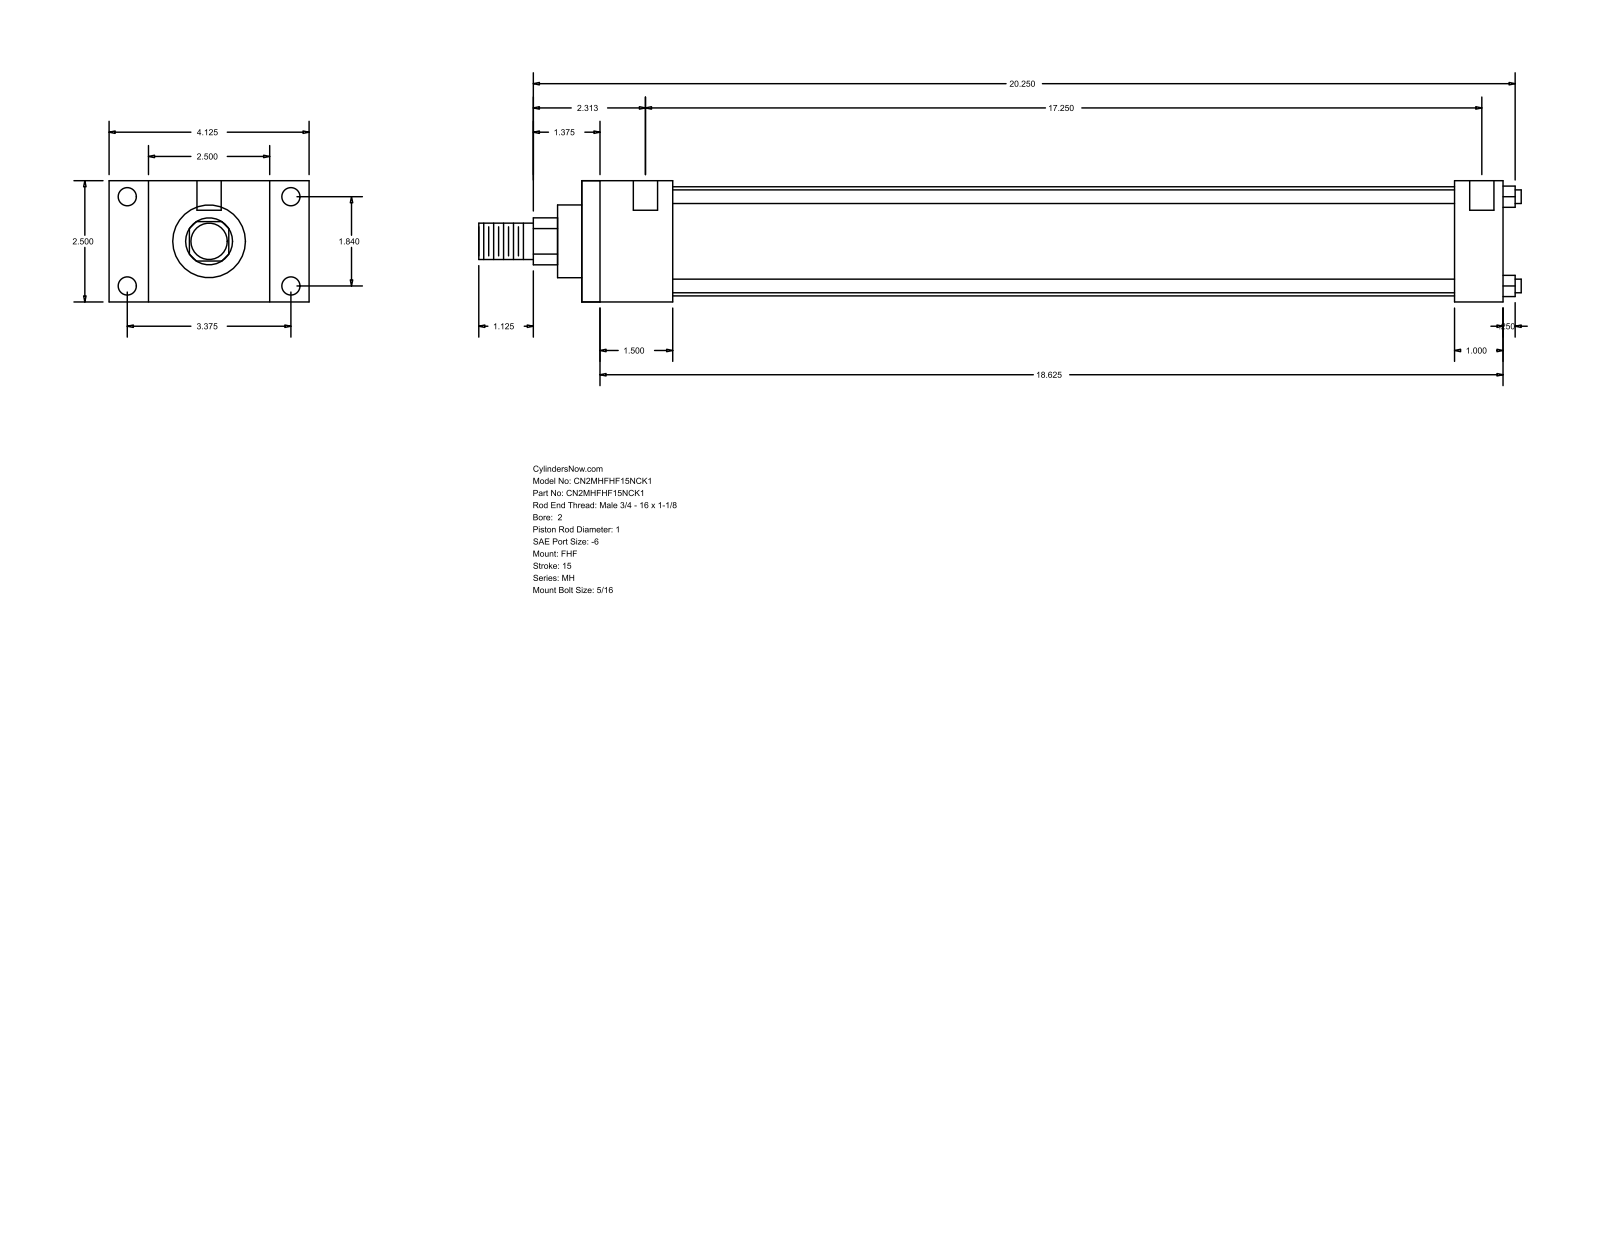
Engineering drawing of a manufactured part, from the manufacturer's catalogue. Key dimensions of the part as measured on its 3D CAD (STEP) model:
Part name (STEP PRODUCT): MH_FHF__0200_1
STEP written by: GSSL Pune (CONFIG_CONTROL_DESIGN)
Units: millimetres
Bodies: 0 solids, 88 faces (60 planar, 28 cylindrical, 0 other)
Overall size (bounding box): 546.1 × 104.78 × 63.5
Round holes (diameter × count): ⌀5.56 ×4, ⌀9.53 ×4, ⌀12.7 ×2
Round bosses / shafts (diameter × count): ⌀7.14 ×4, ⌀57.15 ×1, ⌀38.1 ×1, ⌀25.4 ×1, ⌀19.05 ×1
Partial cylindrical surfaces — rounded edges, fillets, slot ends (radius × count): R12.29 ×1
Main face-to-face distances: 63.5, 482.6, 47.63, 434.97, 20.64, 84.14, 104.78, 25.4, 457.2, 409.57
Hole centre spacings: 46.74, 85.72, 97.63, 446.08, 3.17, 4.76, 438.15, 441.32
